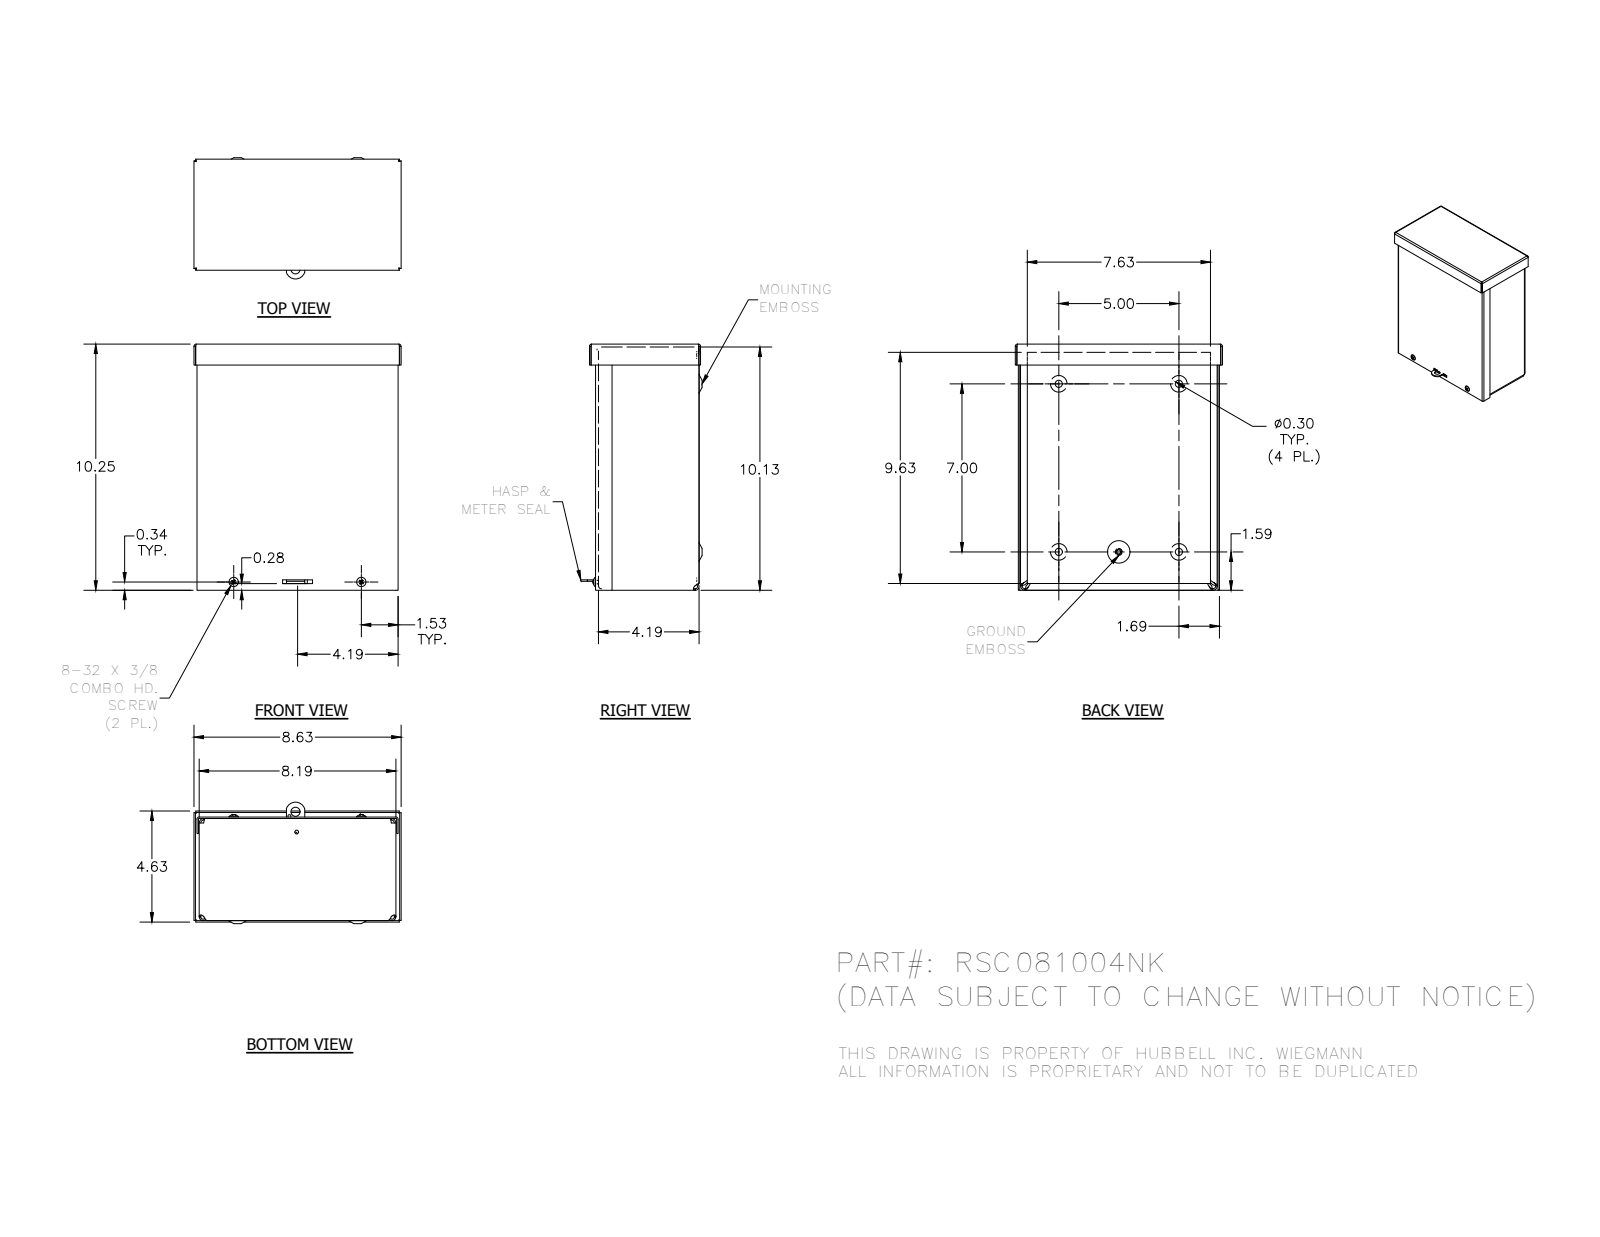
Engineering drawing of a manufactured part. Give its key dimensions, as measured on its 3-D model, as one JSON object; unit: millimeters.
{"part_name": "RSC081004NK_WRAP; RSC0810NK_LID; RSC0804NK_CAP; 3183 (+3 more)", "step_written_by": "Autodesk Inventor 2014 (AUTOMOTIVE_DESIGN)", "units": "millimeters", "bodies": {"solids": 7, "faces": 377, "planar": 163, "cylindrical": 78, "other": 136}, "overall_size": [260.36, 219.07, 130.17], "volume_mm3": 438686, "surface_area_mm2": 565575, "round_holes": [[7.62, 4], [7.95, 4], [3.76, 2], [3.17, 1], [3.45, 1], [3.96, 1], [4.19, 1], [9.52, 1]], "round_bosses_or_shafts": [[9.75, 2], [4.17, 2], [5.8, 1]], "partial_cylinders_radius": [[0.79, 8], [2.37, 8], [3.17, 8], [4.75, 8], [1.4, 4], [1.57, 4], [2.38, 4], [2.97, 4]], "face_to_face_distances": [1.58, 1.57, 107.93, 106.35, 206.39, 1.59, 109.52, 107.94, 257.19, 3.15], "hole_center_spacings": [27.24, 32.03, 63.5, 127, 134.95, 177.8, 188.79, 204.79]}
